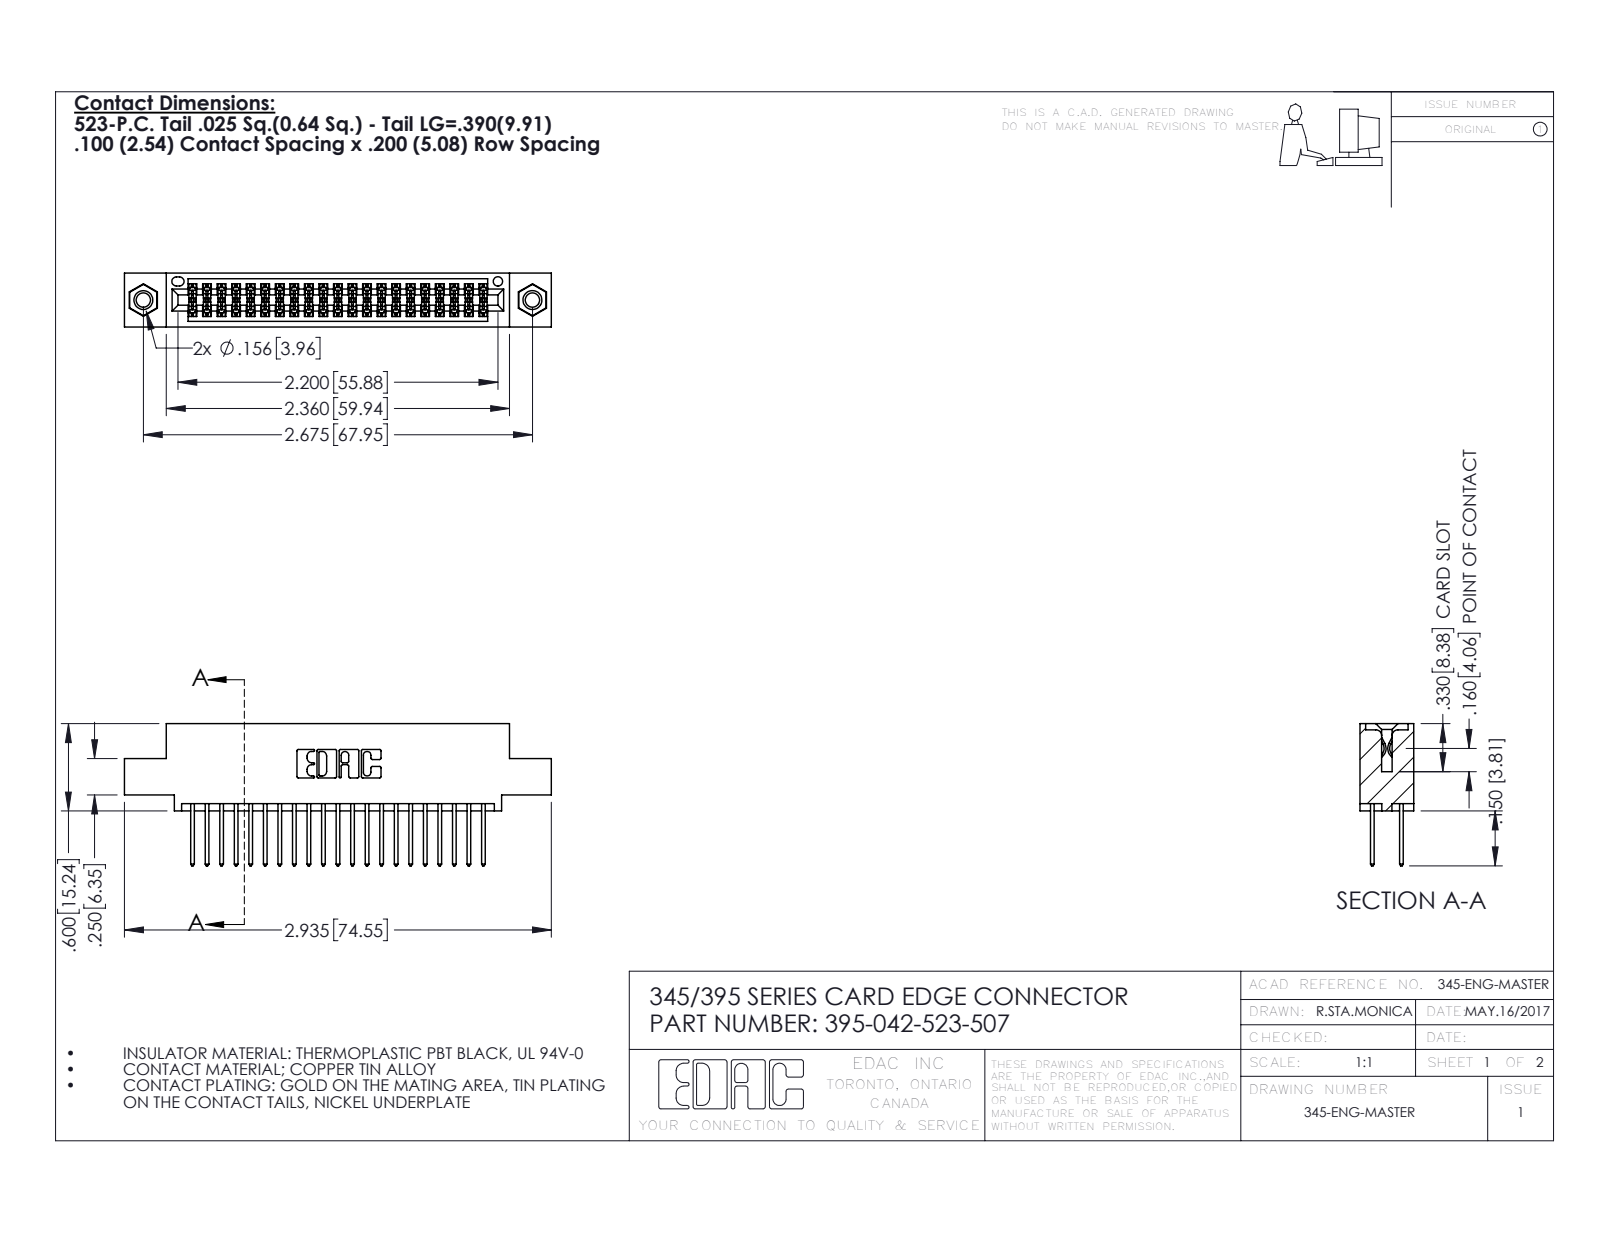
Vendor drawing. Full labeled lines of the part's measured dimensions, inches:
Part name (STEP PRODUCT): 345-292-001_345-293-123; 345-250-001_345-250-005-103; 395-042-523-507; 345 Part_0.110 Offset - 0.156 Dia-TI
STEP written by: SolidWorks 2016 (CONFIG_CONTROL_DESIGN)
Units: inches
Bodies: 45 solids, 2290 faces (1502 planar, 772 cylindrical, 16 other)
Overall size (bounding box): 2.935 × 0.977 × 0.37
Volume: 0.43 in³ · Surface area: 16.3 in²
Round holes (diameter × count): ⌀0.098 ×2, ⌀0.125 ×2, ⌀0.156 ×2, ⌀0.064 ×1
Round bosses / shafts (diameter × count): ⌀0.155 ×2
Partial cylindrical surfaces — rounded edges, fillets, slot ends (radius × count): R0.006 ×63, R0.01 ×42, R0.01 ×22, R0.007 ×6, R0.031 ×6, R0.026 ×3, R0.014 ×2, R0.019 ×2
Main face-to-face distances: 0.072, 0.298, 0.2, 0.098, 0.272, 0.025, 0.37, 0.225, 0.175, 0.149
Hole centre spacings: 0.27, 2.441, 2.675
